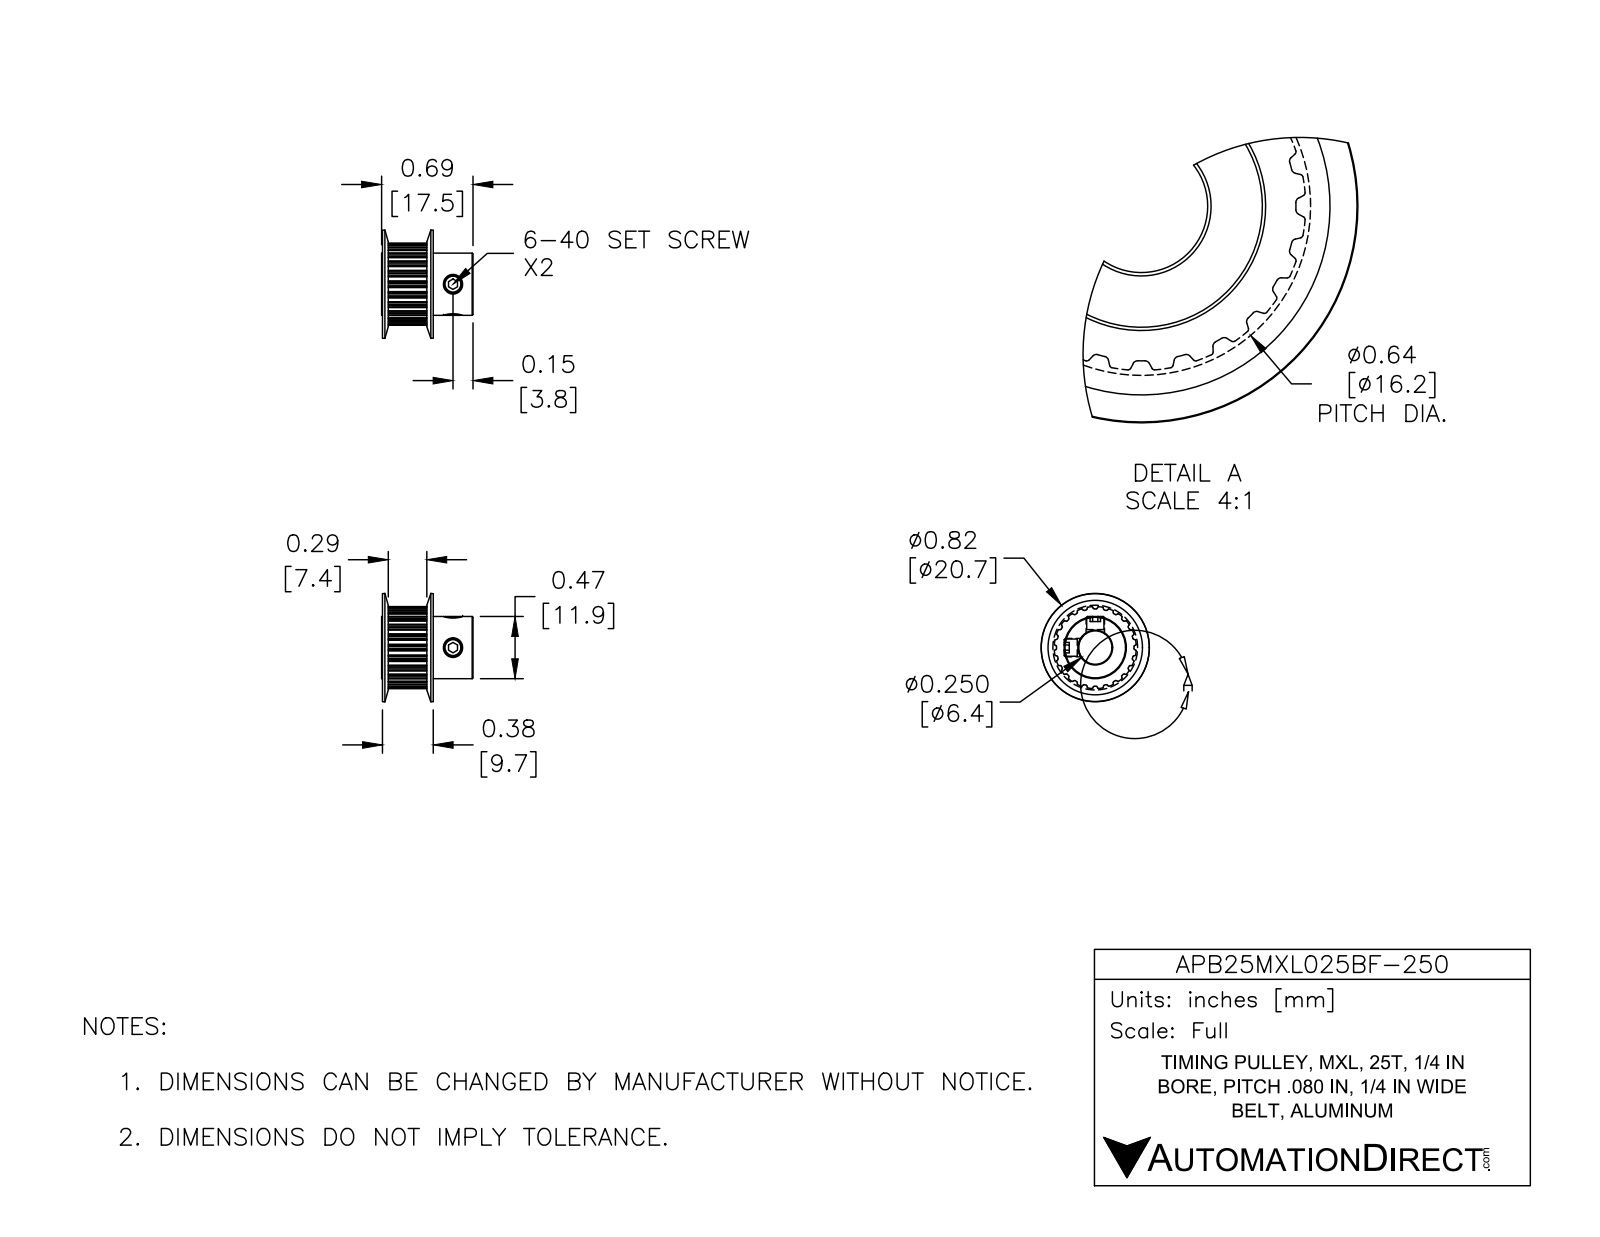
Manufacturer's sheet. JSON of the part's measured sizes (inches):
{"part_name": "APB25MXL025BF-250", "step_written_by": "SolidWorks 2016 (AUTOMOTIVE_DESIGN)", "units": "inches", "bodies": {"solids": 3, "faces": 277, "planar": 72, "cylindrical": 179, "other": 26}, "overall_size": [0.815, 0.815, 0.687], "volume_in3": 0.132, "surface_area_in2": 3.433, "round_holes": [[0.138, 2], [0.25, 1]], "round_bosses_or_shafts": [[0.13, 2], [0.468, 1]], "partial_cylinders_radius": [[0.005, 48], [0.009, 48], [0.291, 1], [0.309, 1]], "face_to_face_distances": [0.346, 0.025, 0.37, 0.687, 0.663, 0.317, 0.251, 0.05, 0.025, 0.32]}
